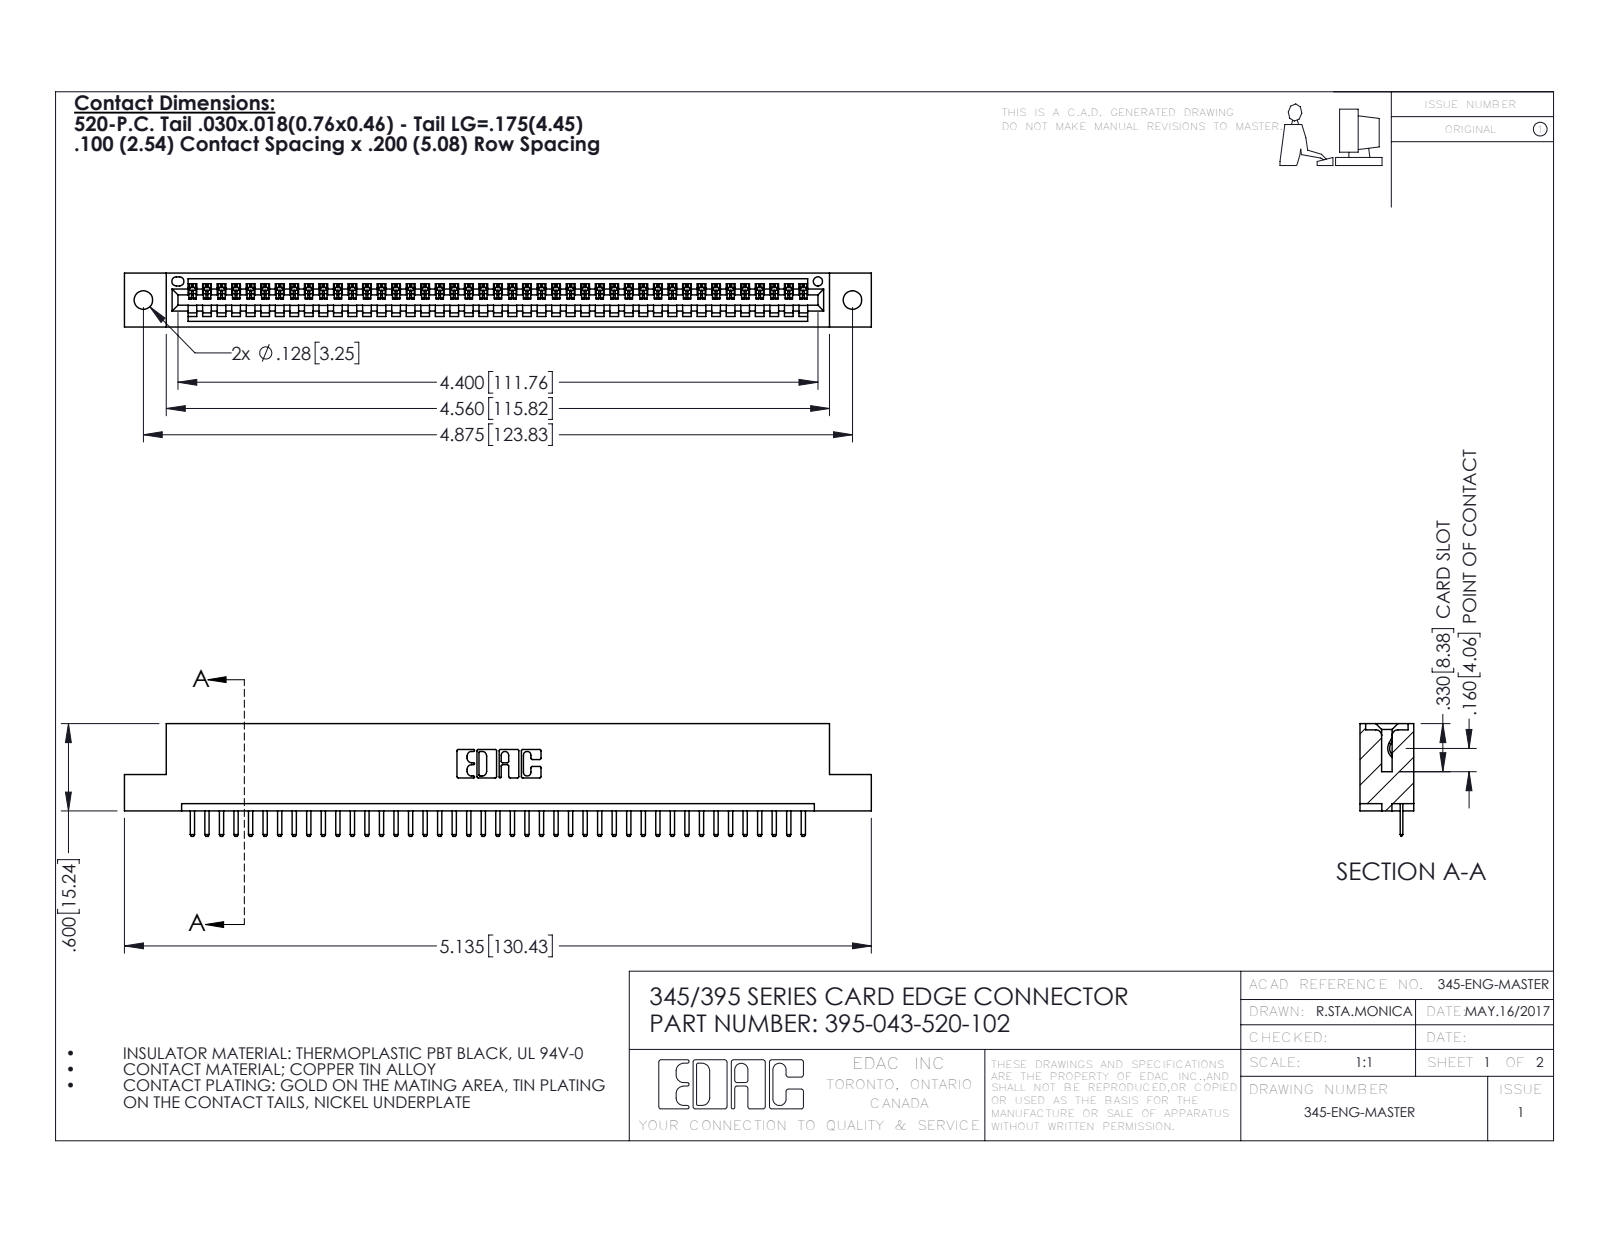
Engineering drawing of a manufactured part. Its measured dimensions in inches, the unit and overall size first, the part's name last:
Units: inches
Overall size (bounding box): 5.135 × 0.775 × 0.37
Round holes (diameter × count): ⌀0.128 ×2, ⌀0.064 ×1
Partial cylindrical surfaces — rounded edges, fillets, slot ends (radius × count): R0.01 ×88, R0.006 ×86, R0.01 ×22, R0.007 ×6, R0.031 ×6, R0.026 ×3, R0.031 ×2, R0.04 ×2
Main face-to-face distances: 0.298, 0.072, 0.37, 0.2, 0.098, 0.272, 0.025, 0.225, 0.072, 0.149
Hole centre spacings: 0.27, 4.639, 4.875
Volume: 0.747 in³ · Surface area: 24.18 in²
Bodies: 44 solids, 2792 faces (1886 planar, 906 cylindrical, 0 other)
Part name (STEP PRODUCT): 395-043-520-102; 345 Part_Flush Mounting Lugs - 0.128 Dia; 345-292-001_345-293-120
STEP written by: SolidWorks 2016 (CONFIG_CONTROL_DESIGN)
